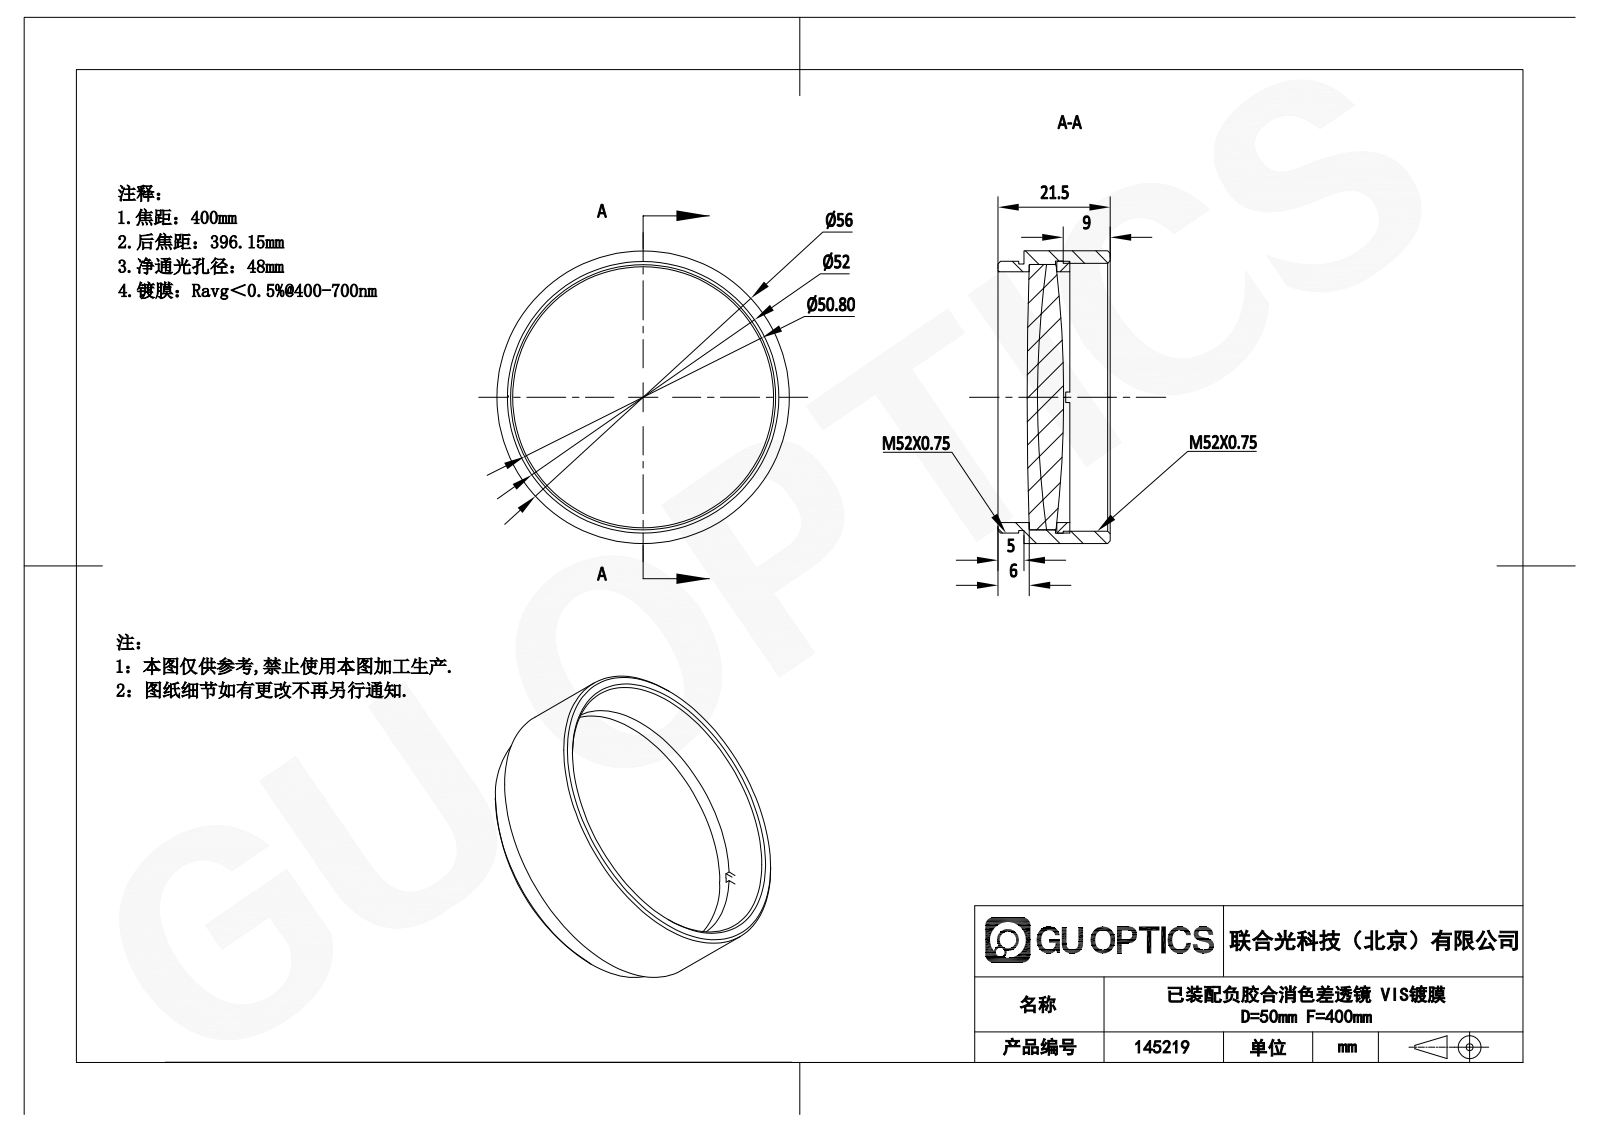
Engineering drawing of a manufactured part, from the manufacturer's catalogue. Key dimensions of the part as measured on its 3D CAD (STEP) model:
Part name (STEP PRODUCT): M52x0.75ѹȦ; APD-ML50-400-VIS; GL31-050B-400-VIS_Solidworks
STEP written by: SolidWorks 2022 (AUTOMOTIVE_DESIGN)
Units: millimetres
Bodies: 4 solids, 58 faces (16 planar, 22 cylindrical, 20 other)
Overall size (bounding box): 56 × 56 × 21.5
Volume: 21 393 mm³ · Surface area: 18 884 mm²
Round holes (diameter × count): ⌀48 ×1, ⌀51.25 ×1, ⌀52.1 ×1
Round bosses / shafts (diameter × count): ⌀56 ×1, ⌀52 ×1, ⌀51 ×1, ⌀50.8 ×1
Main face-to-face distances: 5, 6, 8.76, 1, 6.26, 2.5, 11.26, 13.76, 21.5, 16.5
